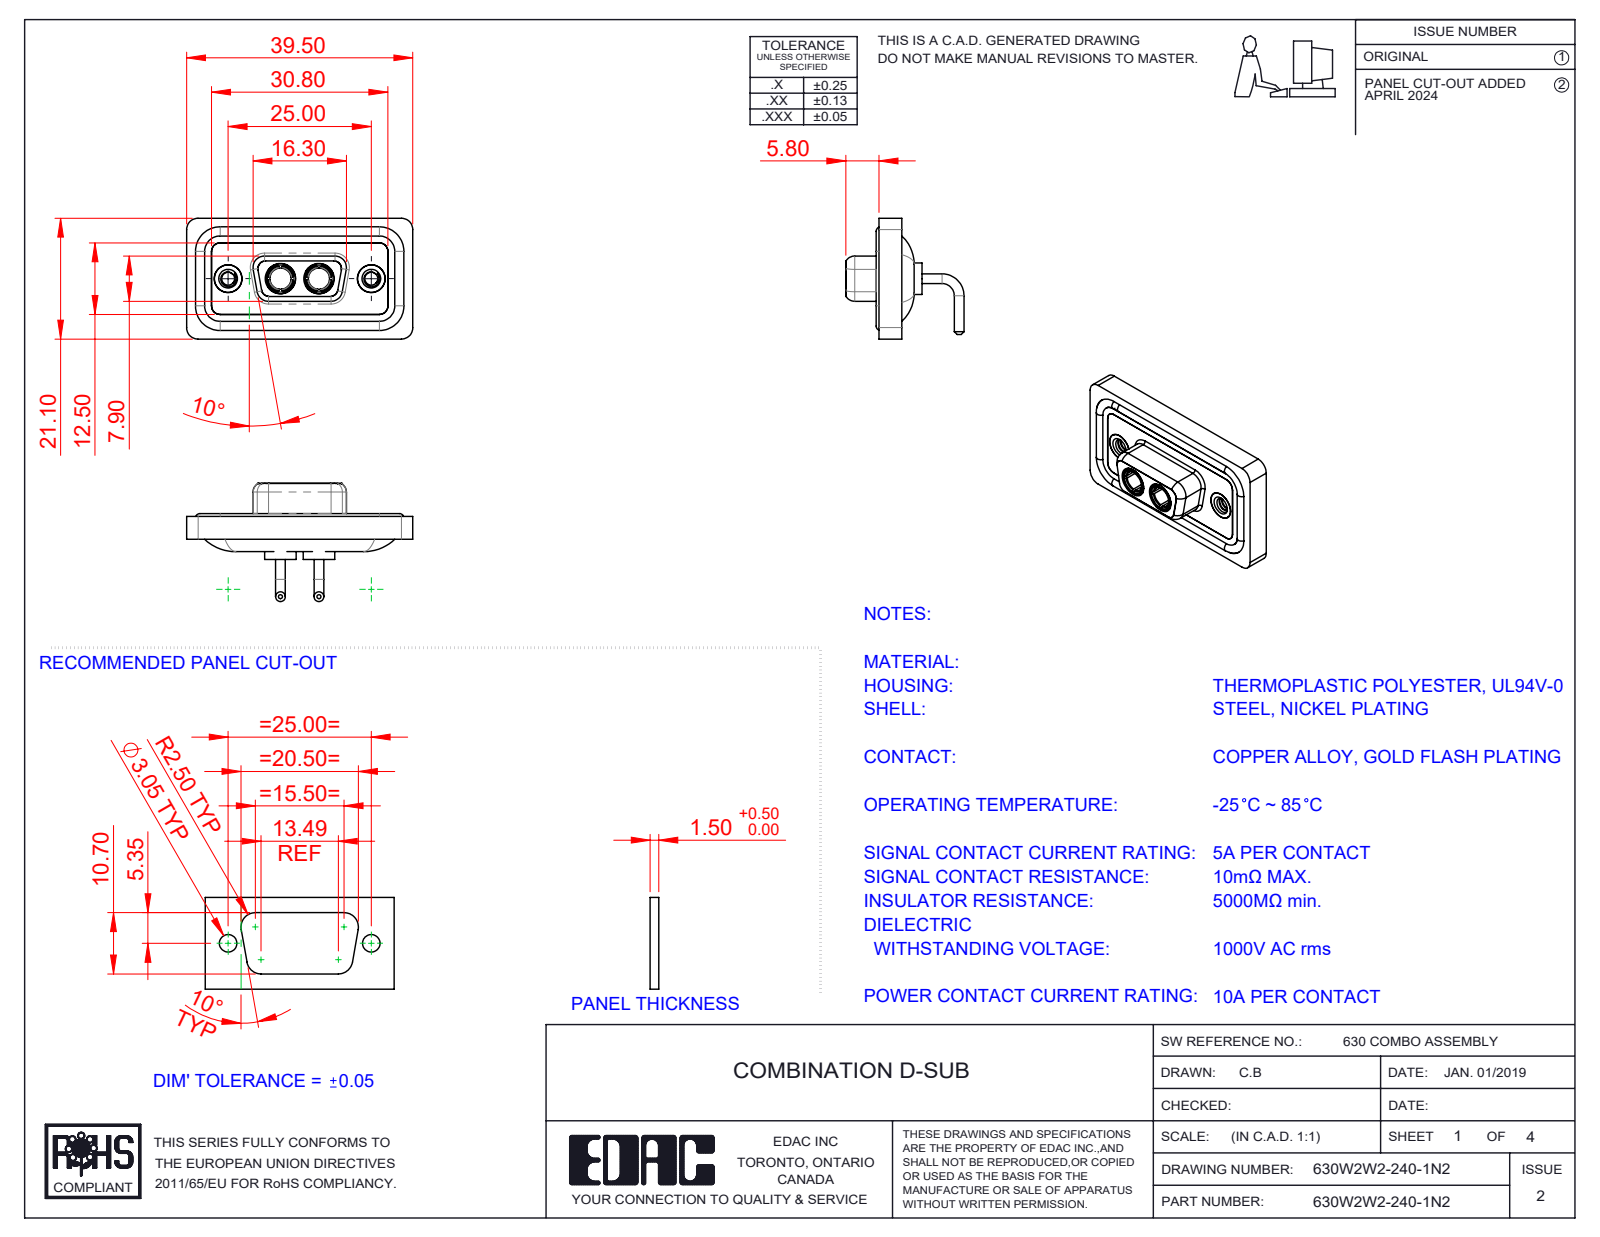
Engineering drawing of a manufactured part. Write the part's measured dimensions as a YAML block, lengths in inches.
part_name: "630W2W2-140-1N2; Power Socket_10A RA; 630Combo Waterproof Housing_09 Contacts; 630Combo Threaded Rivet_2 (+3 more)"
step_written_by: "SolidWorks 2023 (CONFIG_CONTROL_DESIGN)"
units: inches
bodies: {solids: 11, faces: 542, planar: 163, cylindrical: 238, other: 141}
overall_size: [1.555, 0.831, 0.813]
volume: 0.287
surface_area: 11.91
round_holes:
  - {diameter: 0.191, count: 4}
  - {diameter: 0.089, count: 2}
  - {diameter: 0.146, count: 2}
  - {diameter: 0.157, count: 2}
  - {diameter: 0.159, count: 2}
  - {diameter: 0.197, count: 2}
  - {diameter: 0.209, count: 2}
round_bosses_or_shafts:
  - {diameter: 0.067, count: 4}
  - {diameter: 0.063, count: 4}
  - {diameter: 0.217, count: 2}
  - {diameter: 0.205, count: 2}
  - {diameter: 0.195, count: 2}
  - {diameter: 0.195, count: 2}
  - {diameter: 0.189, count: 2}
  - {diameter: 0.187, count: 2}
partial_cylinders:
  - {radius: 0.059, count: 18}
  - {radius: 0.079, count: 18}
  - {radius: 0.053, count: 8}
  - {radius: 0.063, count: 8}
  - {radius: 0.01, count: 4}
  - {radius: 0.02, count: 4}
  - {radius: 0.024, count: 4}
  - {radius: 0.026, count: 4}
face_to_face_distances: [0.016, 0.071, 0.043, 0.114, 0.098, 0.063, 0.122, 0.059, 0.083, 0.02]
hole_center_spacings: [0.36, 0.624, 0.265, 0.984]
